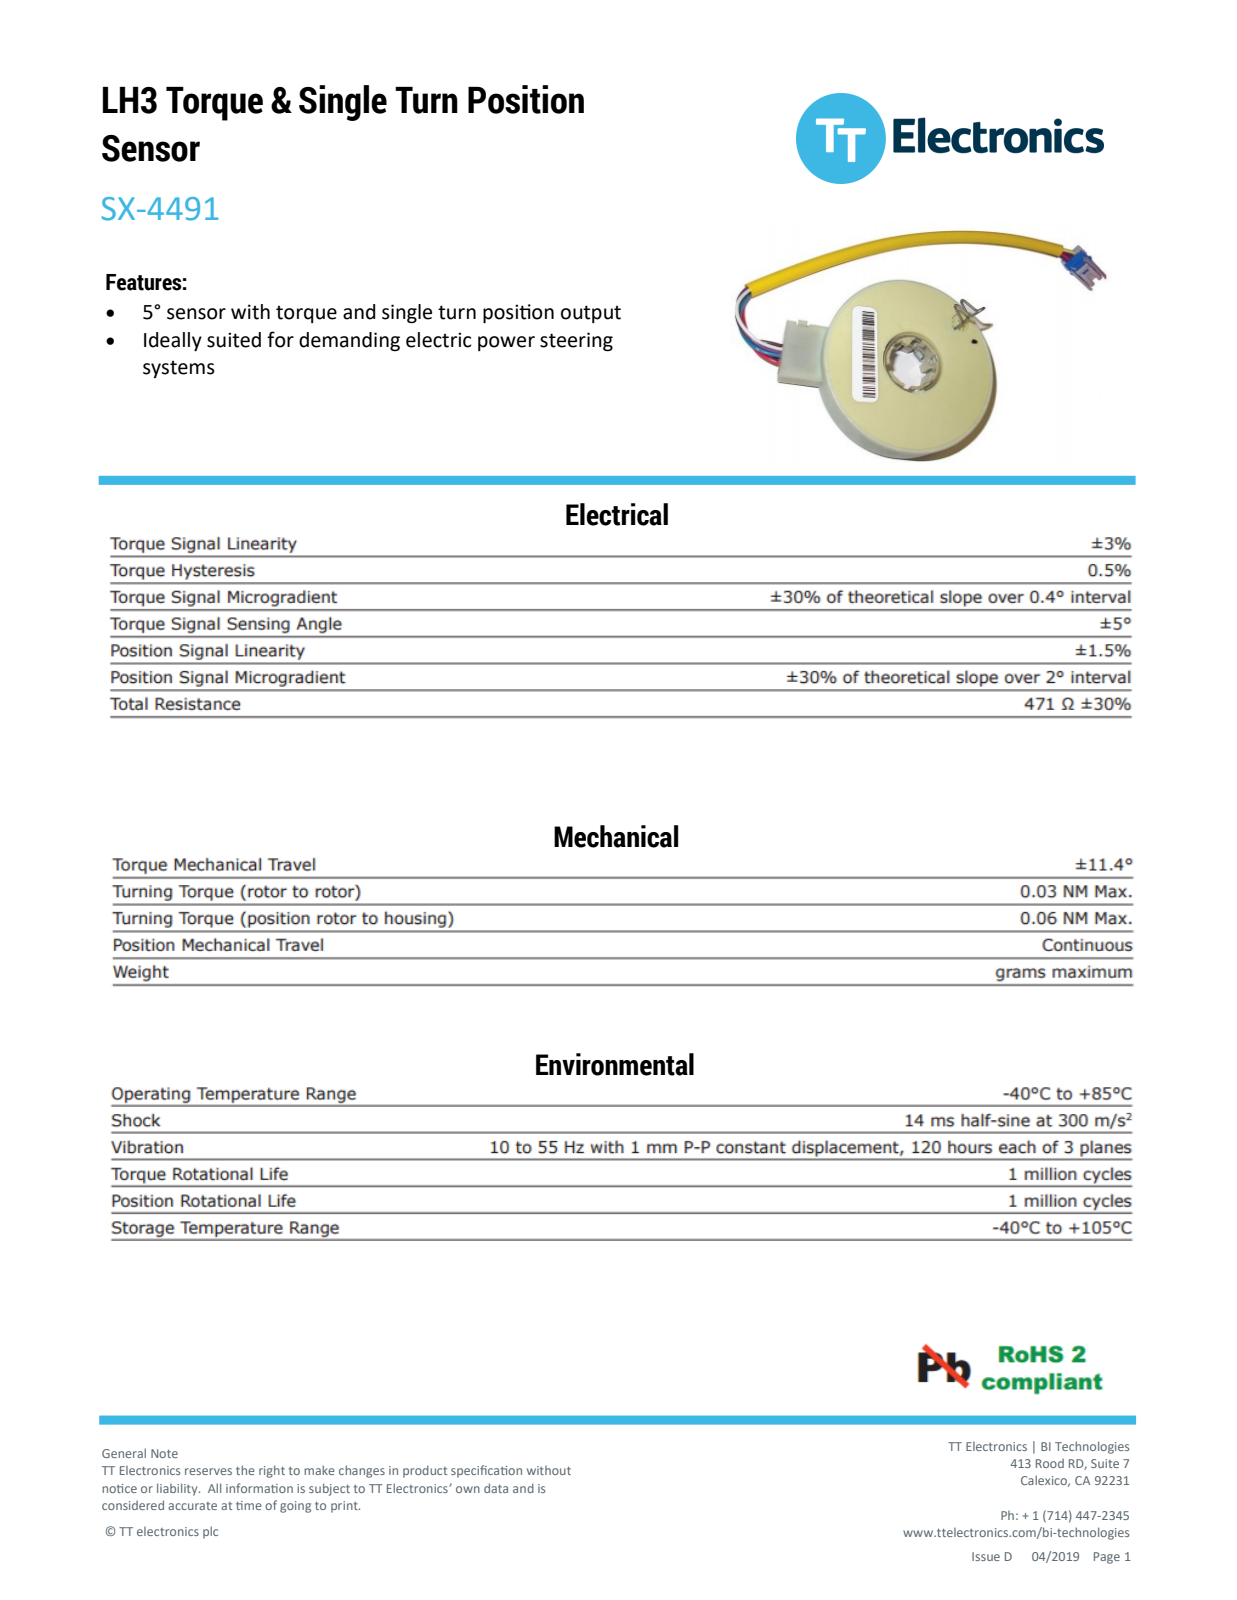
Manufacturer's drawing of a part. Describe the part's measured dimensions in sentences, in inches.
The part is named "SX-4491A_SW0001". Its 3-D file was written by "CREO PARAMETRIC BY PTC INC, 2014500 (CONFIG_CONTROL_DESIGN)". It is 5 solids with 1966 faces: 913 planar, 723 cylindrical and 330 other. Overall it measures 12.313 by 3.2 by 1.728 inches. Its volume is 5.792 cubic inches and its surface area 67.51 square inches. Round holes: 14 of diameter 0.04, 8 of diameter 0.062, 6 of diameter 0.02, 1 of diameter 0.985, 1 of diameter 1.046, 1 of diameter 1.126, 1 of diameter 1.146, 1 of diameter 1.241, 1 of diameter 1.247, 1 of diameter 1.255, 1 of diameter 1.349, 1 of diameter 2.57. Round bosses or shafts: 18 of diameter 0.062, 12 of diameter 0.025, 6 of diameter 0.094, 6 of diameter 0.064, 6 of diameter 0.047, 1 of diameter 3.2, 1 of diameter 1.345, 1 of diameter 1.24. Partial cylindrical surfaces (rounded edges, fillets, slot ends): 72 of radius 0.007, 72 of radius 0.012, 60 of radius 0.01, 44 of radius 0.005, 23 of radius 0.02, 19 of radius 0.016, 18 of radius 0.006, 18 of radius 0.028. The main face-to-face distances are 0.719, 0.05, 0.669, 0.055, 0.664, 0.521, 0.12, 0.055, 0.108, 0.531. The hole center spacings are 0.1, 0.115, 0.141, 0.2, 0.224, 0.23, 0.345, 0.46.
